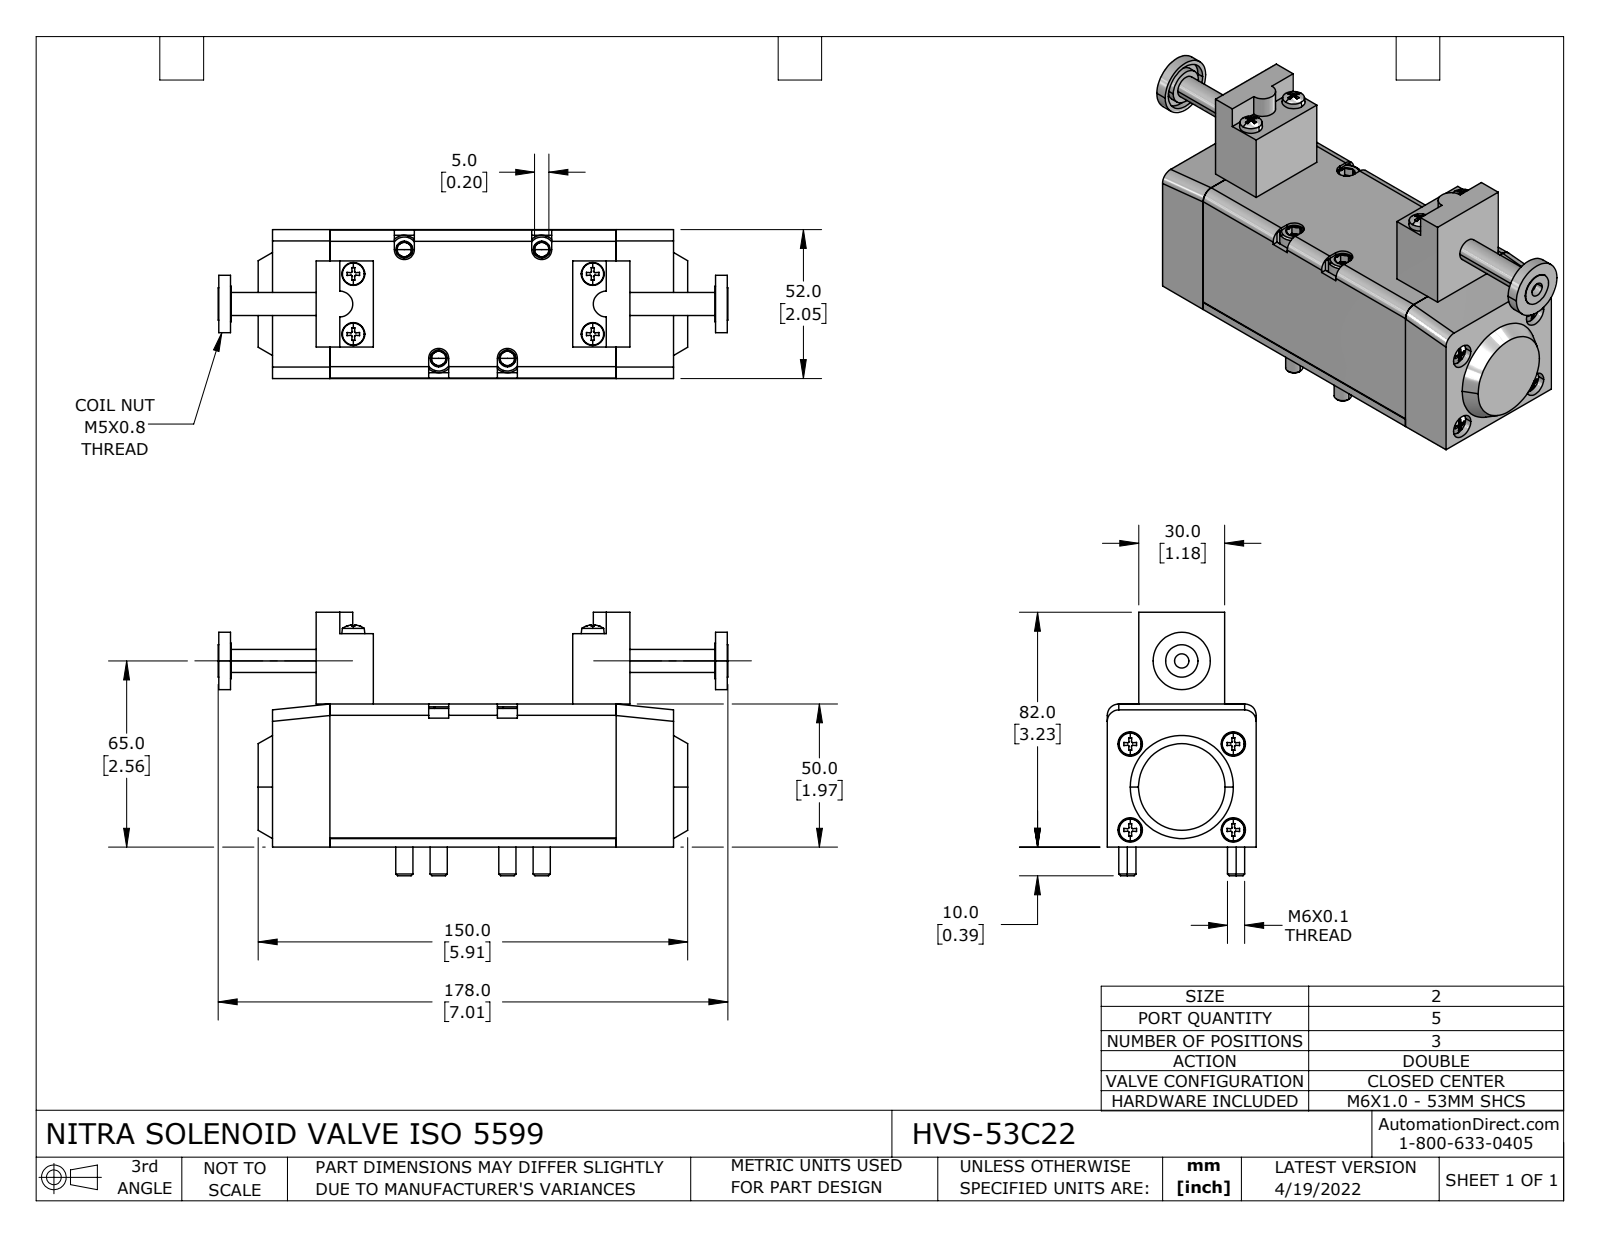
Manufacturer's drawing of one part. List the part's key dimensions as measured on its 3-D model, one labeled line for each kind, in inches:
Part name (STEP PRODUCT): HVS-53C22
STEP written by: SolidWorks 2021 (CONFIG_CONTROL_DESIGN)
Units: inches
Bodies: 21 solids, 850 faces (434 planar, 156 cylindrical, 260 other)
Overall size (bounding box): 7.008 × 3.622 × 2.047
Volume: 24.75 in³ · Surface area: 119.3 in²
Round holes (diameter × count): ⌀0.128 ×8, ⌀0.161 ×4, ⌀0.256 ×4, ⌀0.335 ×4, ⌀0.197 ×1, ⌀0.665 ×1
Round bosses / shafts (diameter × count): ⌀0.157 ×8, ⌀0.394 ×4, ⌀0.236 ×4, ⌀0.787 ×1, ⌀0.488 ×1, ⌀0.445 ×1, ⌀0.315 ×1
Partial cylindrical surfaces — rounded edges, fillets, slot ends (radius × count): R0.157 ×6, R0.138 ×4, R0.197 ×4, R0.177 ×2
Main face-to-face distances: 1.969, 3.937, 2.039, 2.043, 0.787, 0.598, 4.126, 4.724, 0.433, 1.614
Hole centre spacings: 0.777, 0.827, 1.181, 1.22, 1.344, 1.356, 1.417, 1.569
